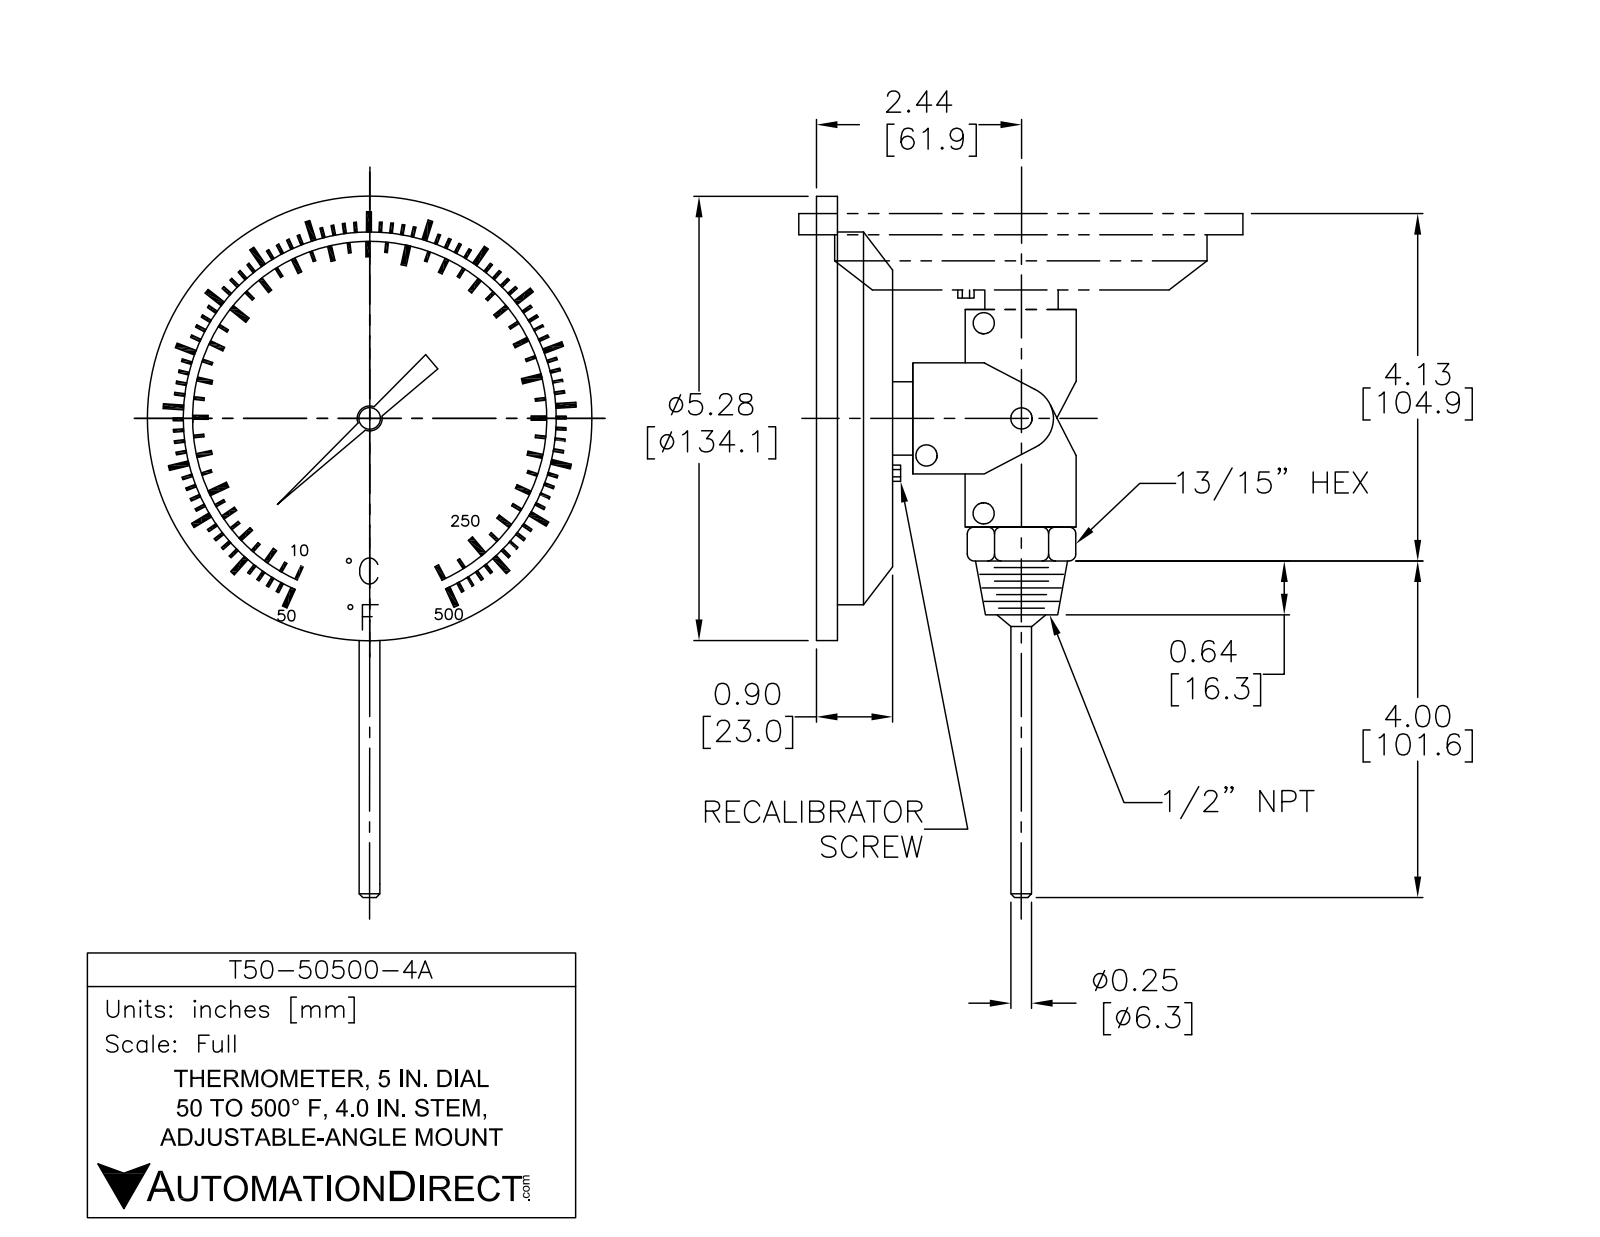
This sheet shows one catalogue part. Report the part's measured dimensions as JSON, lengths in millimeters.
{"part_name": "T50-50500-4A", "step_written_by": "SolidWorks 2021 (AUTOMOTIVE_DESIGN)", "units": "millimeters", "bodies": {"solids": 1, "faces": 494, "planar": 282, "cylindrical": 45, "other": 167}, "overall_size": [202.2, 134.1, 134.1], "volume_mm3": 166000, "surface_area_mm2": 62450, "round_holes": [[87, 1], [94.1, 1], [120.9, 1], [122.8, 1]], "round_bosses_or_shafts": [[7.7, 4], [3.7, 2], [134.1, 1], [126.2, 1], [87.7, 1], [21.6, 1], [20.9, 1], [13.8, 1]], "partial_cylinders_radius": [[1.5, 10], [1, 4], [4.3, 1], [8.5, 1], [8.5, 1], [8.7, 1], [10.2, 1], [47.4, 1]], "face_to_face_distances": [9, 1.9, 1.4, 10.8, 30.2, 20.7, 11.7, 9.9, 31.6, 61.8]}
